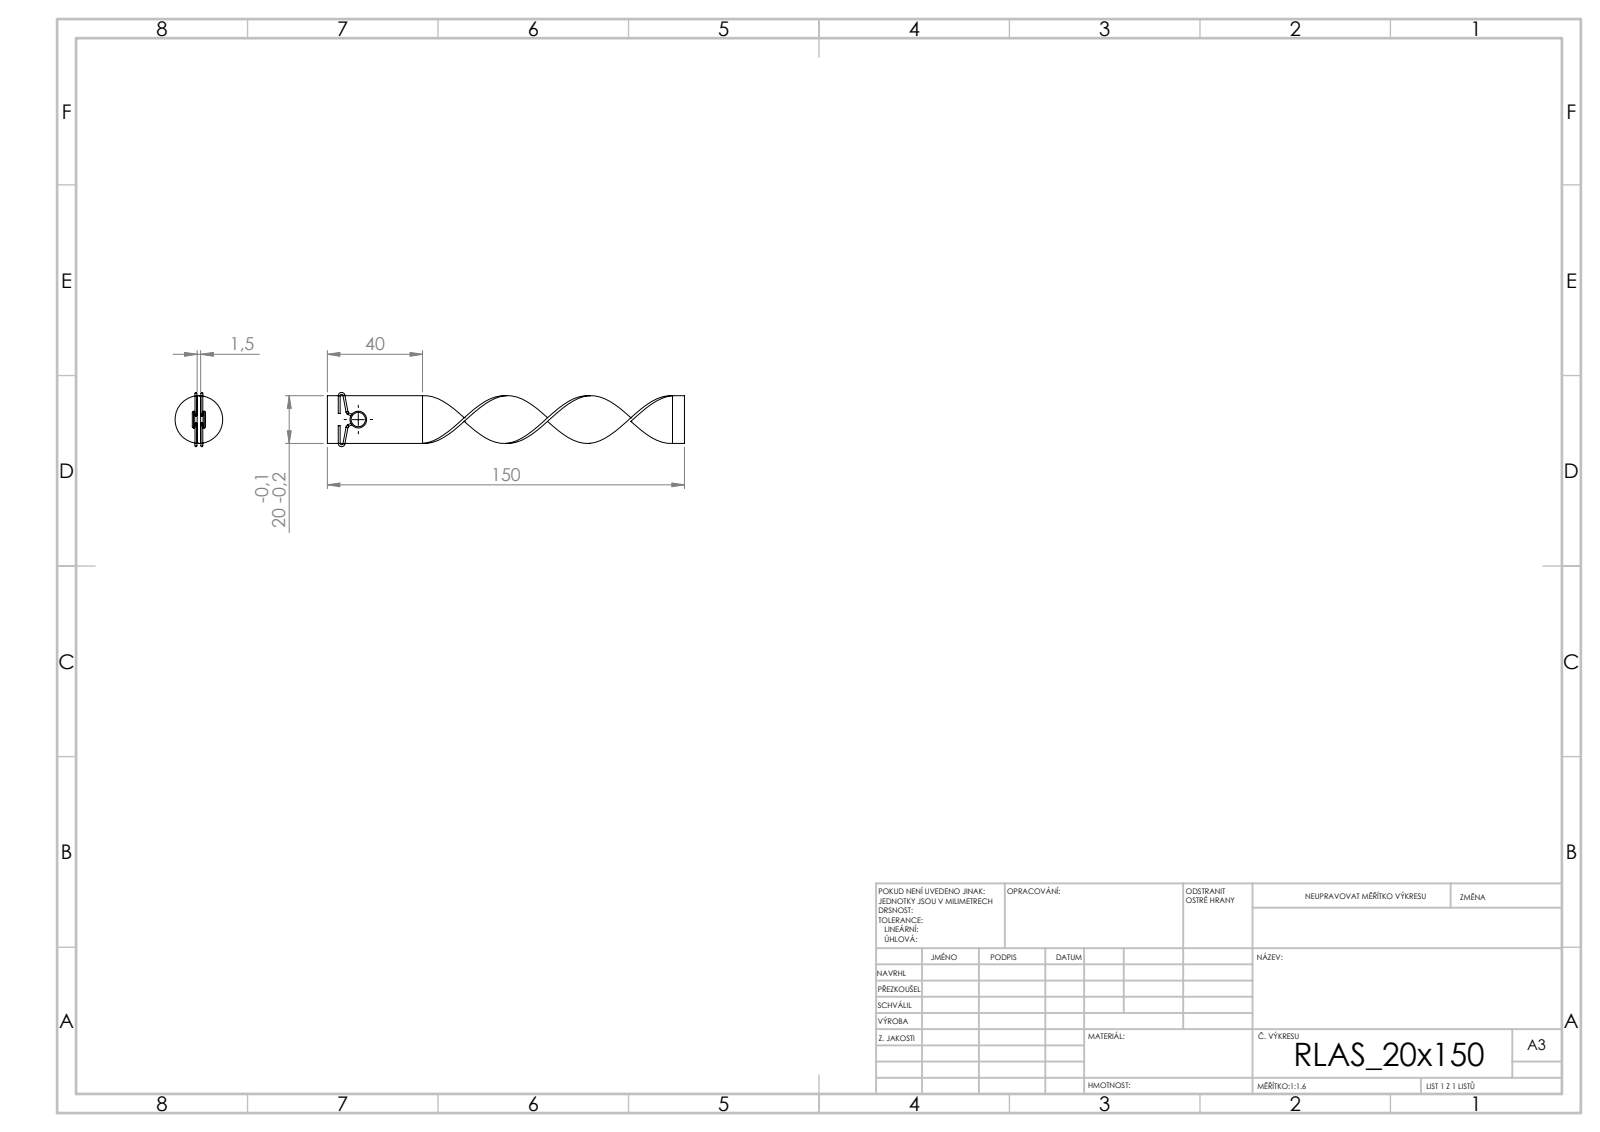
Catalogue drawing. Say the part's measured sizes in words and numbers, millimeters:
Its 3-D file was written by "SolidWorks 2019 (CONFIG_CONTROL_DESIGN)". It is 3 solids with 90 faces: 18 planar, 40 cylindrical and 32 other. Overall it measures 150 by 22.8 by 20.06 millimeters. Its volume is 4 655 cubic millimeters and its surface area 7 458 square millimeters. Round bosses or shafts: 14 of diameter 0.8, 1 of diameter 7, 1 of diameter 4. The main face-to-face distances are 1.5, 1, 3.5, 20, 2, 4.5, 2.5, 150, 5.5, 7.45.
